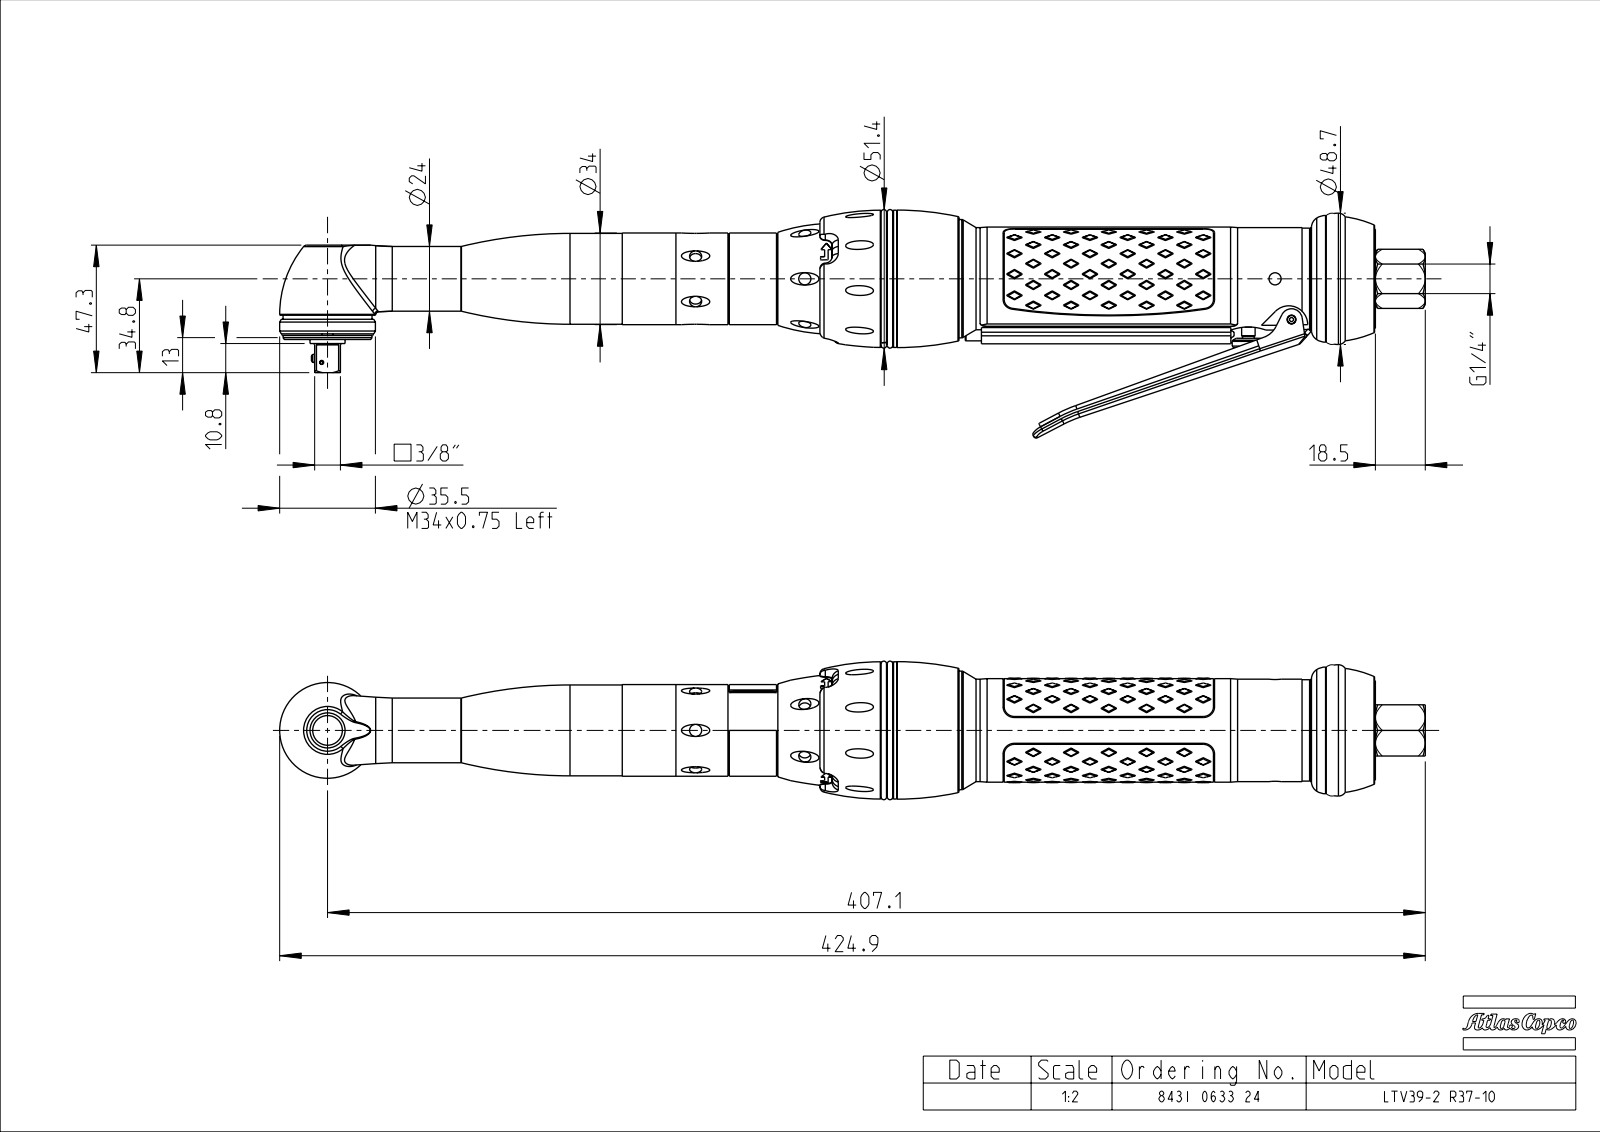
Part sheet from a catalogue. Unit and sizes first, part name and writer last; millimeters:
Units: millimetres
Overall size (bounding box): 424.85 × 84.76 × 51.4
Round holes (diameter × count): ⌀4.5 ×4, ⌀5 ×3, ⌀5.2 ×1, ⌀8 ×1, ⌀11 ×1, ⌀15 ×1, ⌀17 ×1, ⌀18.5 ×1, ⌀19.9 ×1, ⌀20 ×1, ⌀20.1 ×1, ⌀22.8 ×1
Round bosses / shafts (diameter × count): ⌀13 ×2, ⌀50.9 ×1, ⌀47 ×1, ⌀44 ×1, ⌀41.75 ×1, ⌀38.4 ×1, ⌀35.8 ×1, ⌀35.5 ×1
Partial cylindrical surfaces — rounded edges, fillets, slot ends (radius × count): R4 ×4, R2.5 ×3, R4.5 ×3, R4.6 ×3, R0.2 ×2, R1 ×2, R2.9 ×2, R19 ×2
Main face-to-face distances: 19, 2.2, 16.8, 205.7, 203.5, 186.7, 57.1, 54.9, 38.1, 148.6
Hole centre spacings: 13.2, 29.41, 6.83, 18.67, 20.5, 22.86, 32.6
Bodies: 0 solids, 529 faces (59 planar, 265 cylindrical, 205 other)
Part name (STEP PRODUCT): TMP17244_SW
STEP written by: PRO/ENGINEER BY PARAMETRIC TECHNOLOGY CORPORATION, 2008310 (CONFIG_CONTROL_DESIGN)
